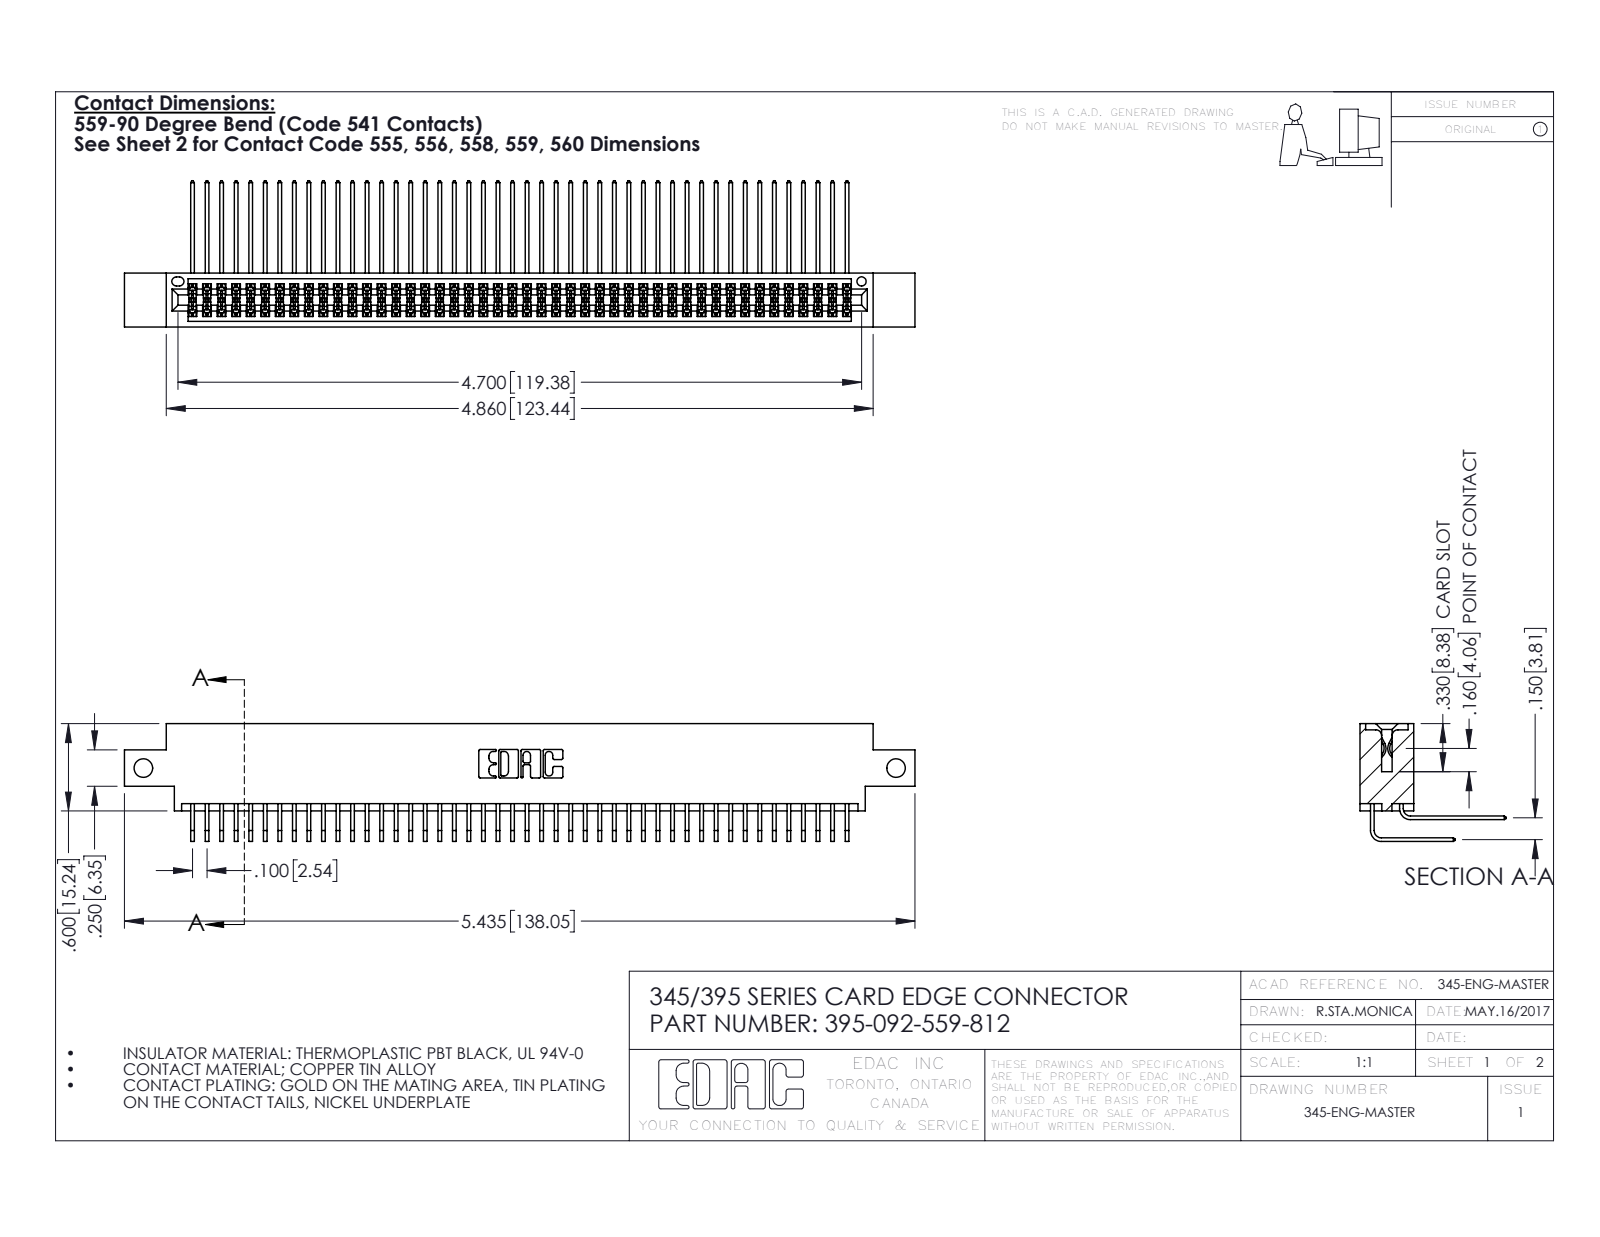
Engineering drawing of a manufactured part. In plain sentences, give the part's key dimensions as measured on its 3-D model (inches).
The part is named "345-292-001_559 Tail - 2; 345-292-001_558 559 Tail - 1; 395-092-559-812; 345 Part_0.170 Offset - Side Mount". Its 3-D file was written by "SolidWorks 2016 (CONFIG_CONTROL_DESIGN)". It is 93 solids with 4914 faces: 3304 planar, 1610 cylindrical and 0 other. Overall it measures 5.435 by 1.005 by 0.809 inches. Its volume is 0.841 cubic inches and its surface area 35.57 square inches. Round holes: 2 of diameter 0.128, 1 of diameter 0.064. Partial cylindrical surfaces (rounded edges, fillets, slot ends): 138 of radius 0.006, 22 of radius 0.01, 6 of radius 0.007, 6 of radius 0.031, 3 of radius 0.026, 2 of radius 0.014, 2 of radius 0.019, 2 of radius 0.022. The main face-to-face distances are 0.072, 0.298, 0.37, 0.2, 0.098, 0.272, 0.025, 0.225, 0.175, 0.15. The hole center spacings are 5.175.
